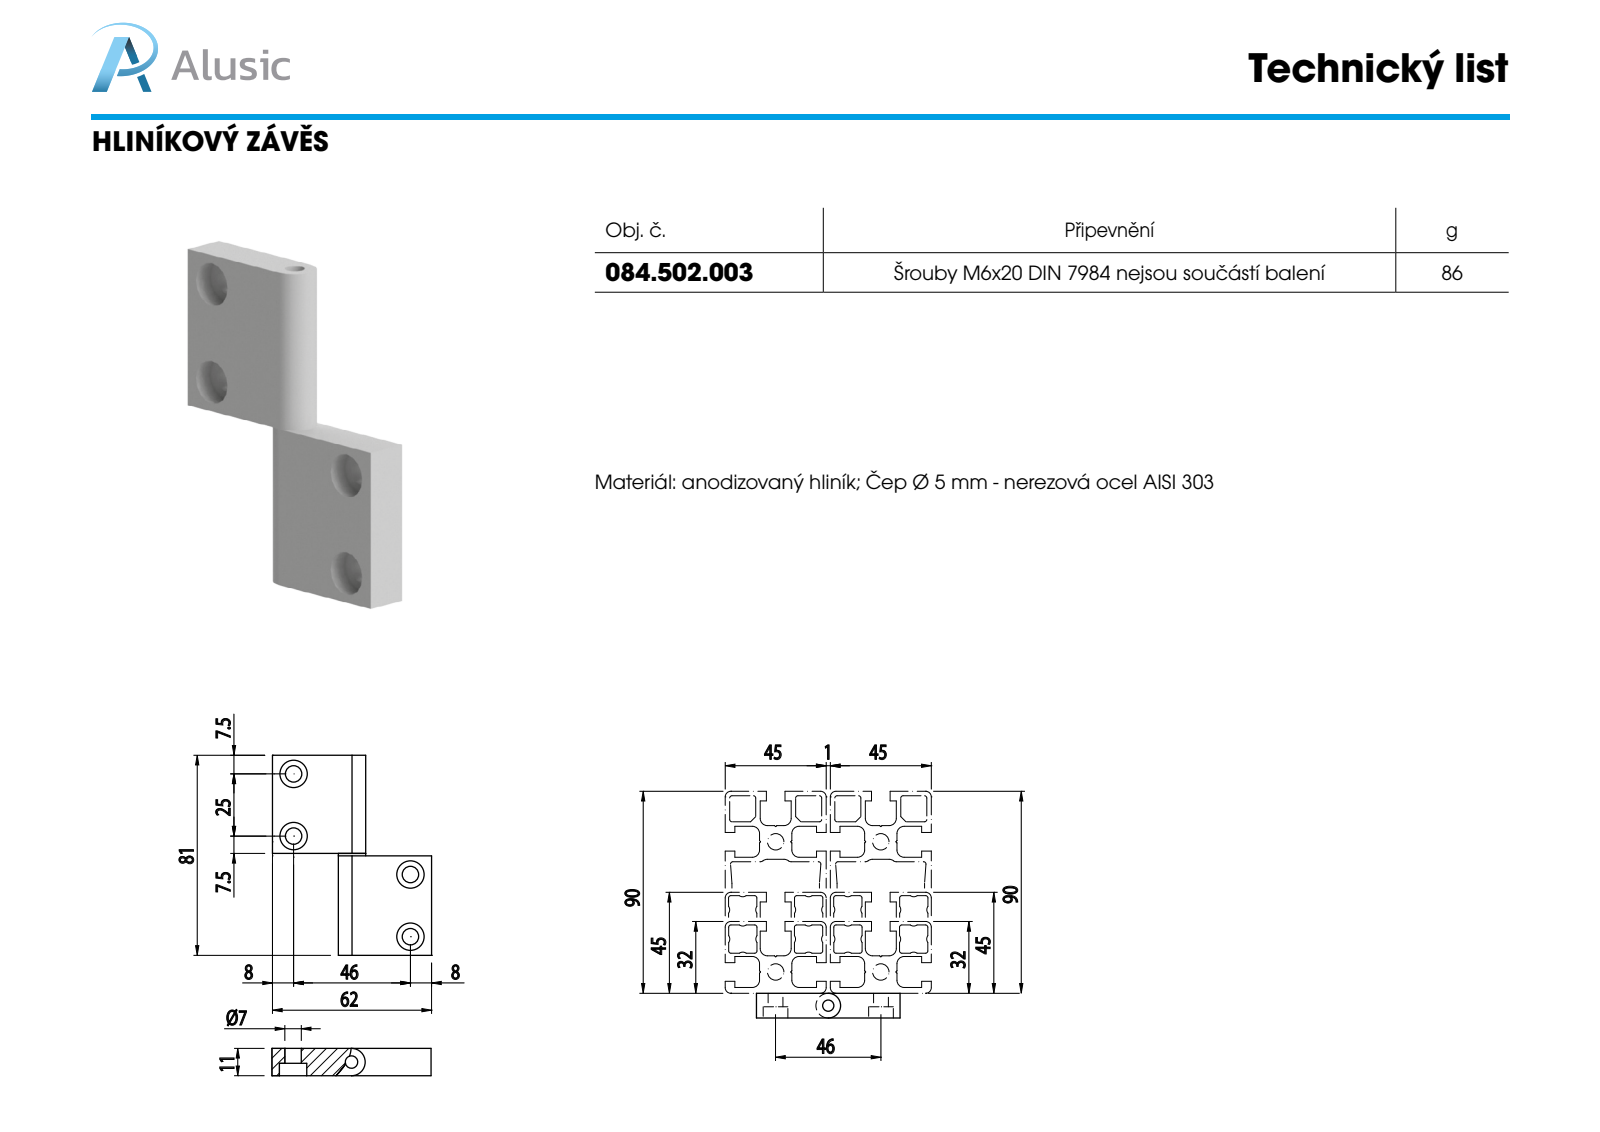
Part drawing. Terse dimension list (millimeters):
name: 084.502.003; 084.502.000 ALETTE_ALETTA 2
written by: SolidWorks 2011 (CONFIG_CONTROL_DESIGN)
unit: mm
bodies: 2 solids, 36 faces (14 planar, 22 cylindrical, 0 other)
size: 80 × 64 × 11
volume: 27 669 mm³; area: 11 074 mm²
holes: 4× ⌀6.6, 4× ⌀11, 1× ⌀5
bosses: 1× ⌀11
face distances: 11, 40, 64, 80, 6, 5
hole spacings: 25, 61.72, 49.34, 80.21
